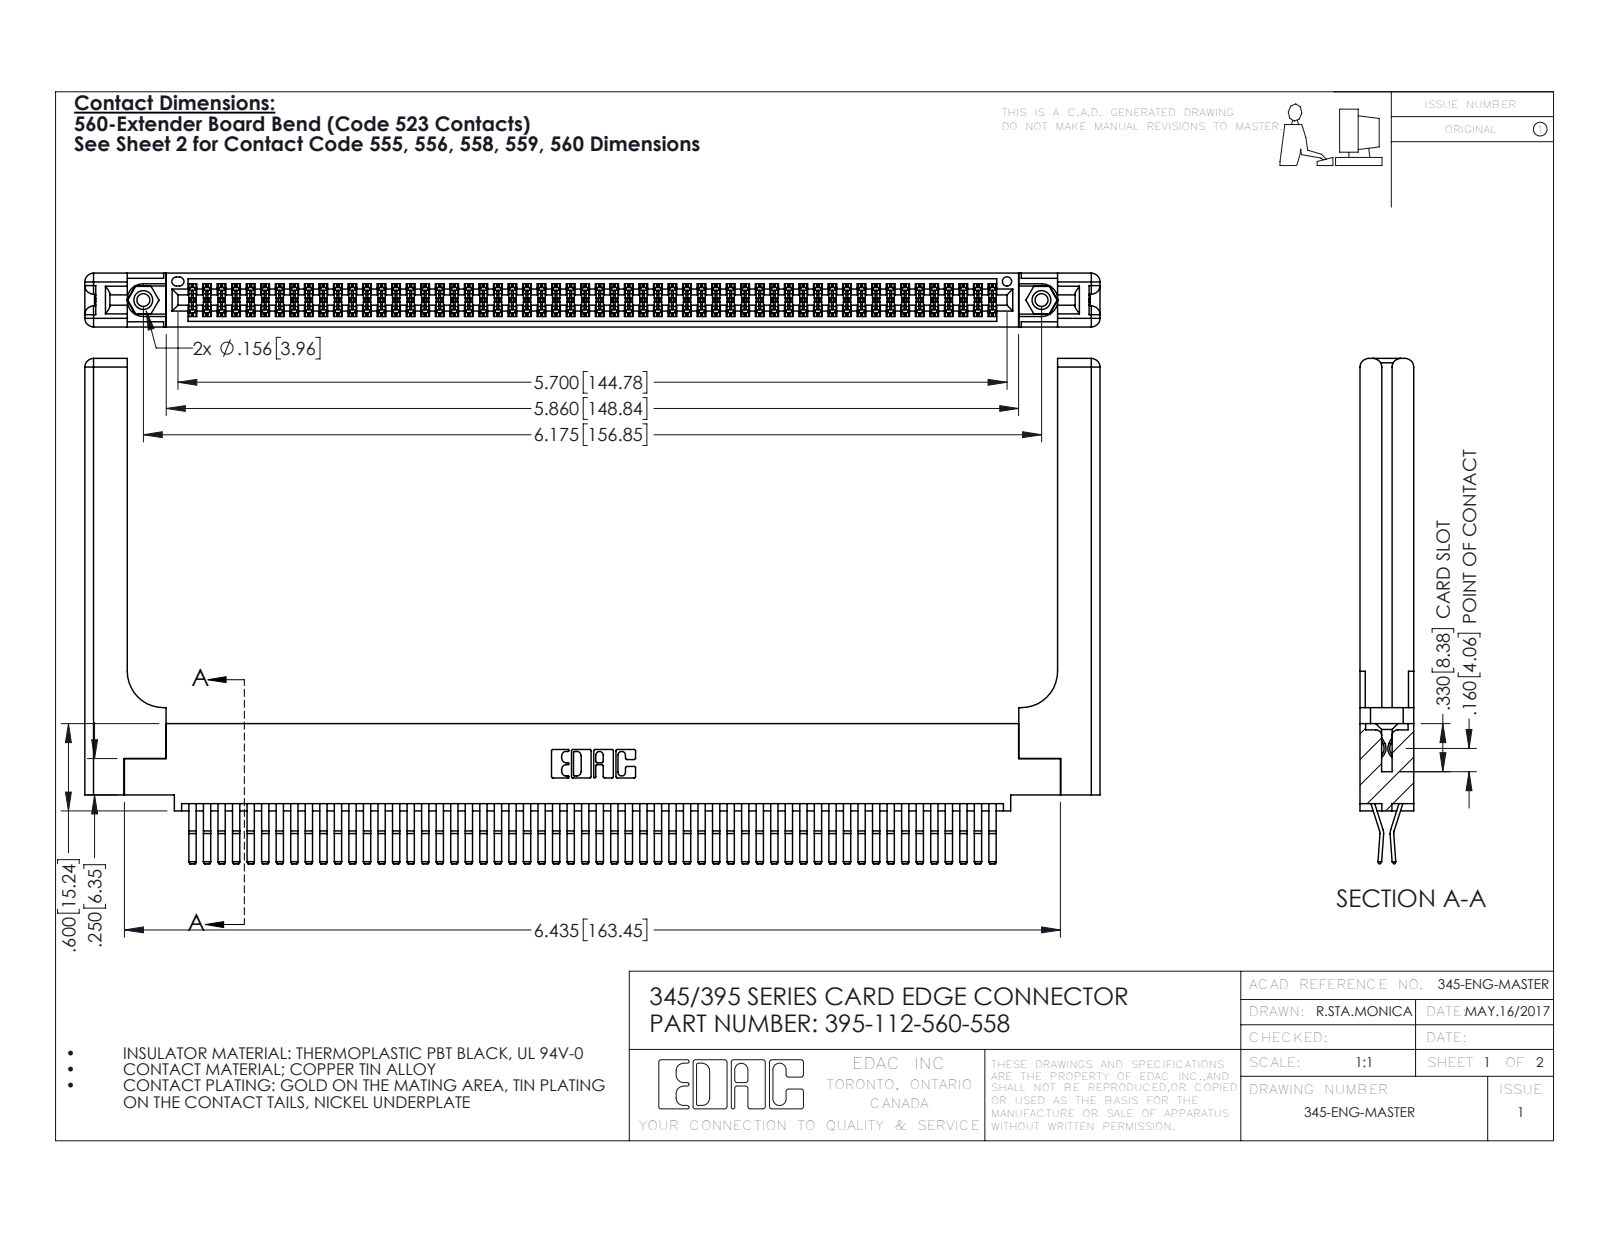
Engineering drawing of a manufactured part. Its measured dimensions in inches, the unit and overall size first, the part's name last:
Units: inches
Overall size (bounding box): 6.979 × 3.472 × 0.37
Round holes (diameter × count): ⌀0.089 ×2, ⌀0.125 ×2, ⌀0.156 ×2, ⌀0.064 ×1
Round bosses / shafts (diameter × count): ⌀0.155 ×2
Partial cylindrical surfaces — rounded edges, fillets, slot ends (radius × count): R0.006 ×168, R0.01 ×22, R0.06 ×16, R0.007 ×6, R0.031 ×6, R0.026 ×3, R0.01 ×2, R0.014 ×2
Main face-to-face distances: 0.072, 0.298, 0.025, 0.37, 0.098, 0.272, 0.2, 0.225, 0.148, 0.15
Hole centre spacings: 0.27, 5.939, 6.175
Volume: 1.616 in³ · Surface area: 52.6 in²
Bodies: 117 solids, 6210 faces (3928 planar, 2222 cylindrical, 60 other)
Part name (STEP PRODUCT): 345-250-001_345-250-001-102; 345 Part_0.110 Offset - 0.156 Dia-TH; 345-220-058_345-220-058; 395-112-560-558 (+1 more)
STEP written by: SolidWorks 2016 (CONFIG_CONTROL_DESIGN)
